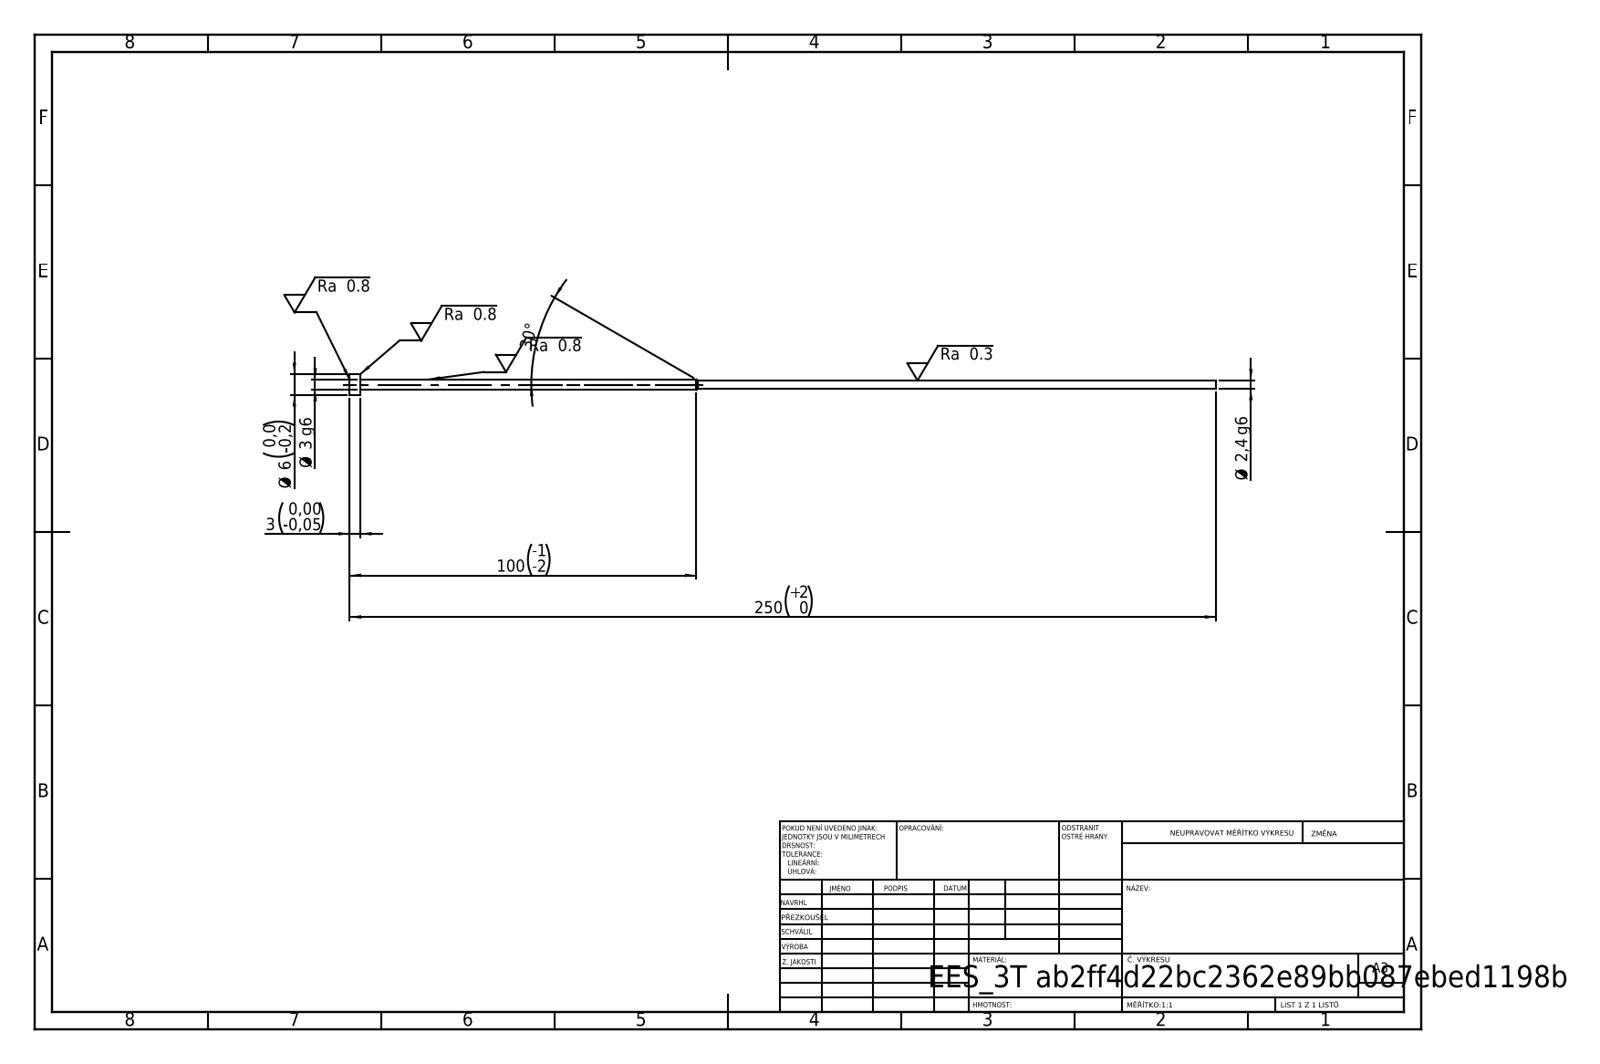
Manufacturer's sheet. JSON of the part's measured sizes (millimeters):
{"step_written_by": "SolidWorks 2019 (CONFIG_CONTROL_DESIGN)", "units": "millimeters", "bodies": {"solids": 1, "faces": 11, "planar": 3, "cylindrical": 6, "other": 2}, "overall_size": [250, 6, 6], "volume_mm3": 1450, "surface_area_mm2": 2157, "round_bosses_or_shafts": [[6, 1], [3, 1], [2.4, 1]], "face_to_face_distances": [3, 247, 250]}
